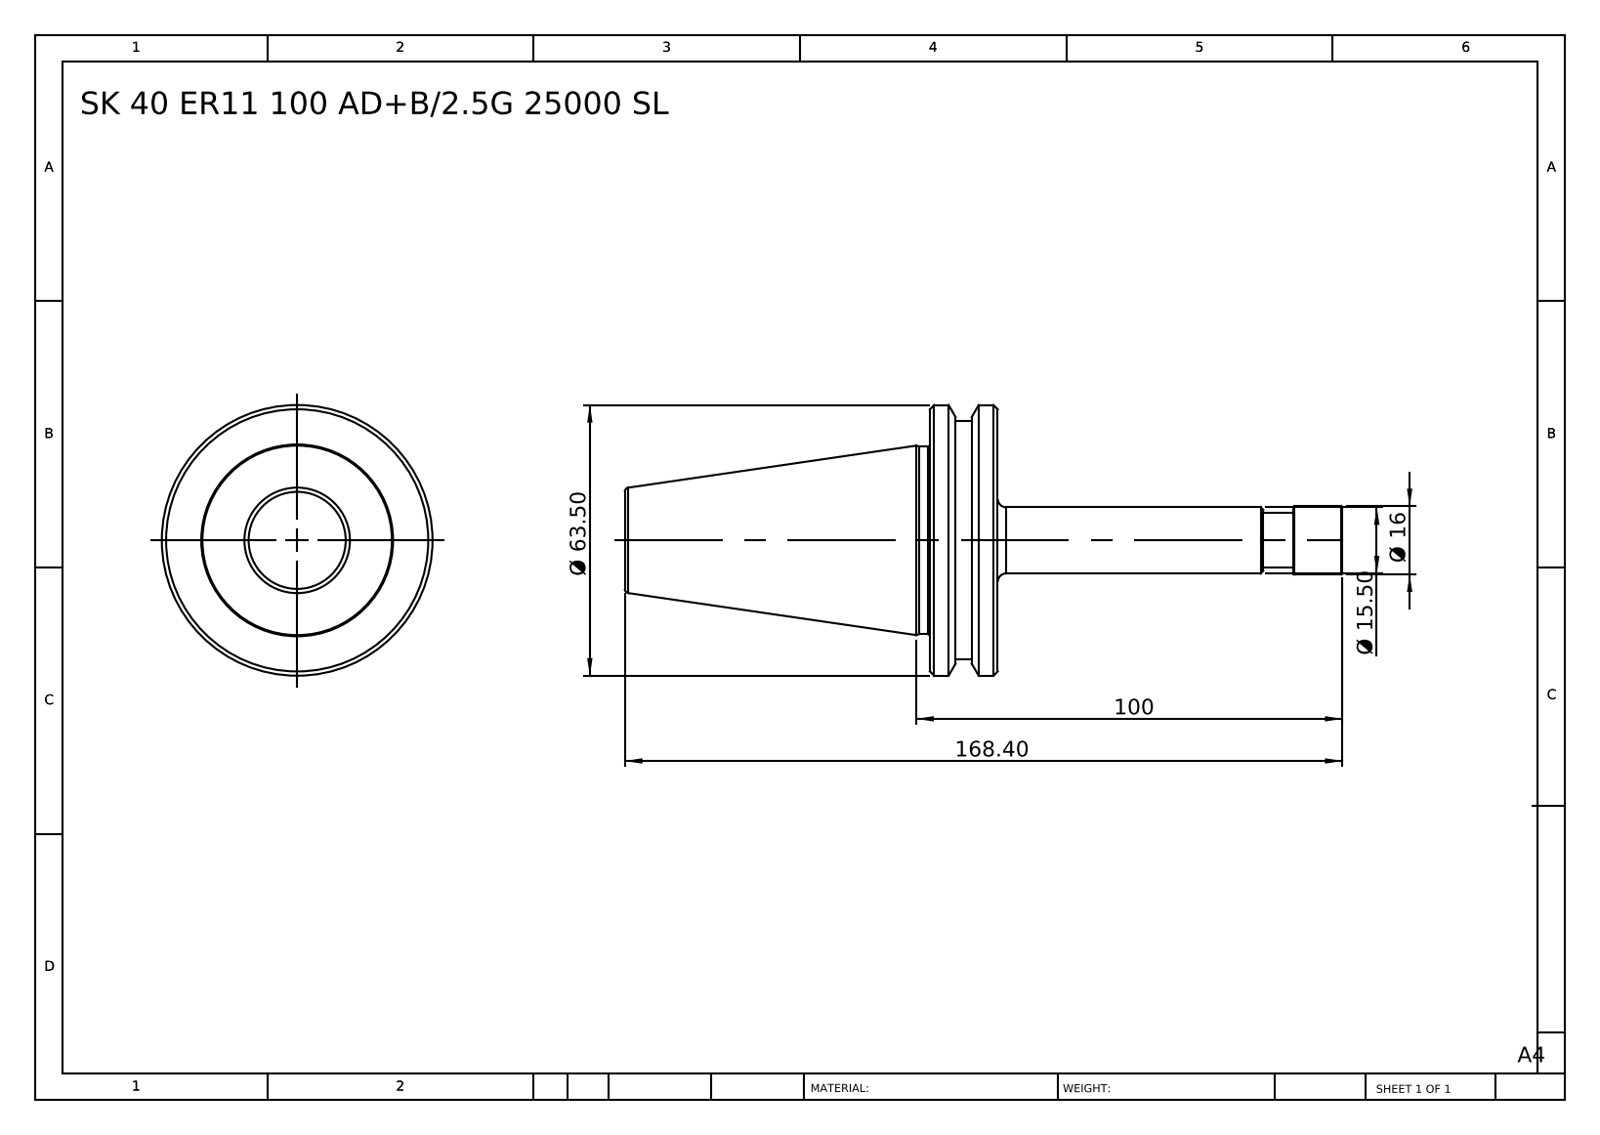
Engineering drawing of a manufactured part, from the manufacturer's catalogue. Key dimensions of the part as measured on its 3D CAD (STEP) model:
Part name (STEP PRODUCT): SK 40 ER11M 100 AD+B-2.5G 25000 SL
STEP written by: SolidWorks 2014 (CONFIG_CONTROL_DESIGN)
Units: millimetres
Bodies: 1 solid, 46 faces (8 planar, 14 cylindrical, 24 other)
Overall size (bounding box): 168.4 × 63.5 × 63.5
Volume: 132 131 mm³ · Surface area: 20 909 mm²
Round bosses / shafts (diameter × count): ⌀63.5 ×1, ⌀56 ×1, ⌀44 ×1, ⌀16 ×1, ⌀15.5 ×1, ⌀12.9 ×1
Main face-to-face distances: 15.9, 87.5, 71.6, 80.9, 96.8, 168.4, 87, 6.1, 9.8, 81.4
